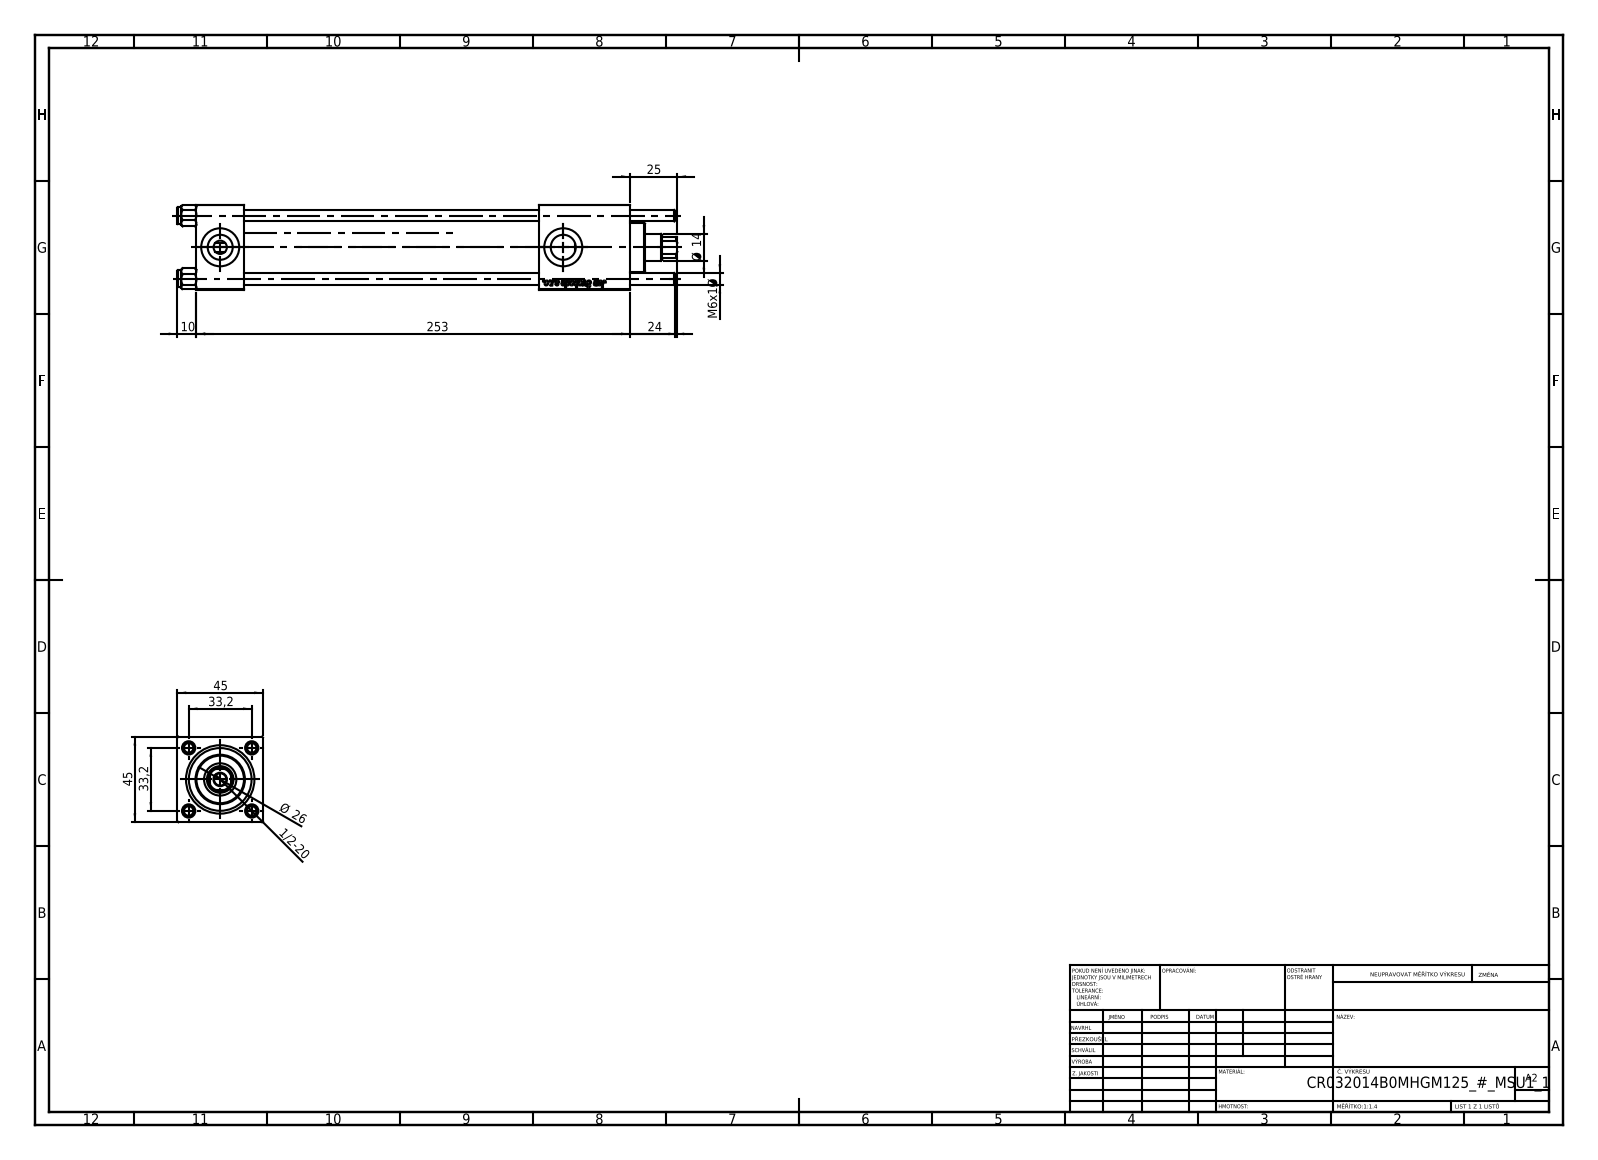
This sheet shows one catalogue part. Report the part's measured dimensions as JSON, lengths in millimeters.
{"part_name": "V215CR_VCP_B; NUT_M5_B; V215CR_B-1; V215_VC_A (+1 more)", "step_written_by": "SolidWorks 2019 (CONFIG_CONTROL_DESIGN)", "units": "millimeters", "bodies": {"solids": 11, "faces": 1157, "planar": 431, "cylindrical": 78, "other": 648}, "overall_size": [263, 45, 45], "volume_mm3": 261046, "surface_area_mm2": 108197, "round_holes": [[6, 4], [7, 2], [13.16, 2], [20, 2], [6.5, 1], [14, 1], [17, 1], [24, 1], [32, 1], [33, 1]], "round_bosses_or_shafts": [[9, 4], [38, 1], [26, 1]], "partial_cylinders_radius": [[6.5, 1]], "face_to_face_distances": [45, 25, 228, 203, 180, 155, 48, 199.3, 174.3, 19.3], "hole_center_spacings": [23.48, 33.2, 46.95, 180.5]}
